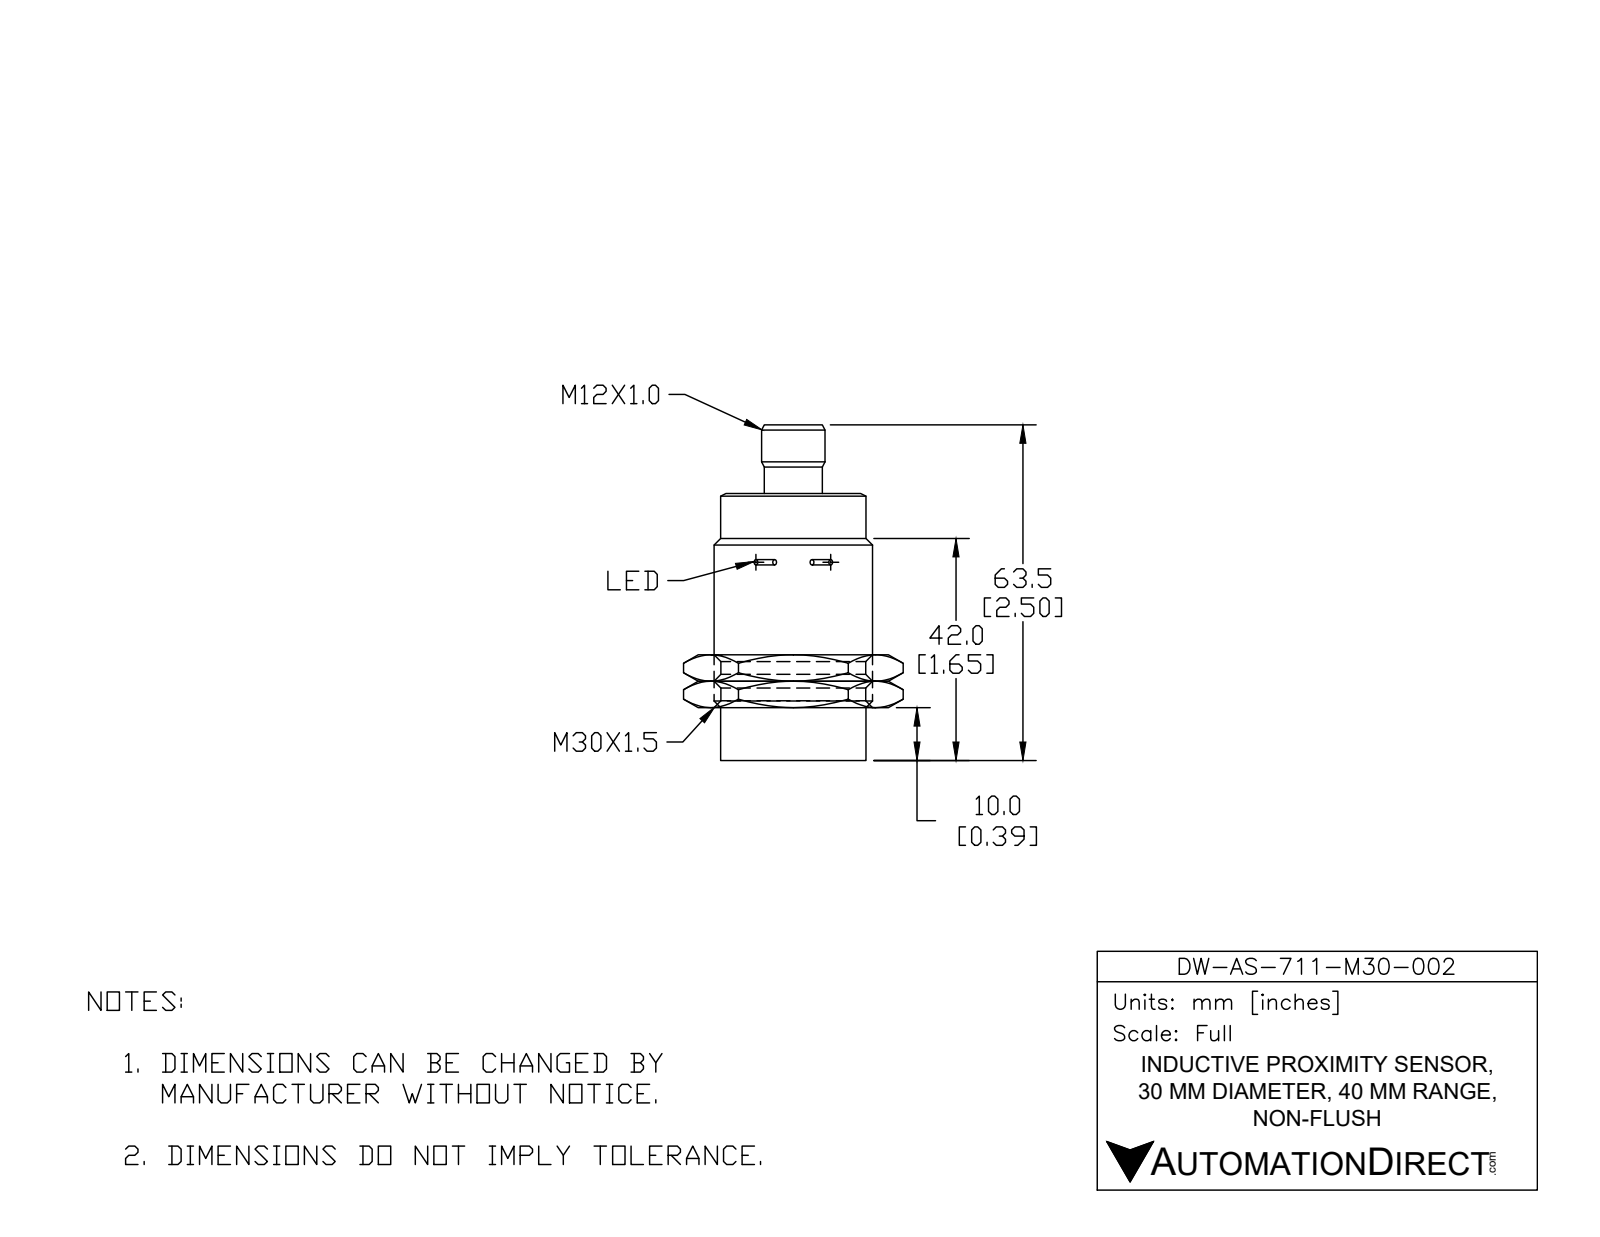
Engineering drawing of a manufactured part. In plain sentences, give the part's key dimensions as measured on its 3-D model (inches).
The part is named "DW-AS-711-M30-002". Its 3-D file was written by "SolidWorks 2017 (AUTOMOTIVE_DESIGN)". It is 1 solid with 51 faces: 14 planar, 27 cylindrical and 10 other. Overall it measures 2.502 by 1.181 by 1.181 inches. Its volume is 2.093 cubic inches and its surface area 10.73 square inches. Round holes: 2 of diameter 0.12, 1 of diameter 0.335. Round bosses or shafts: 4 of diameter 0.043, 1 of diameter 1.181, 1 of diameter 1.083, 1 of diameter 0.472, 1 of diameter 0.415. Partial cylindrical surfaces (rounded edges, fillets, slot ends): 2 of radius 0.019, 1 of radius 0.022, 1 of radius 0.178, 1 of radius 0.193. The main face-to-face distances are 1.988, 2.159, 0.171, 1.654, 0.335, 0.506, 0.394, 1.26, 1.594, 1.766.
